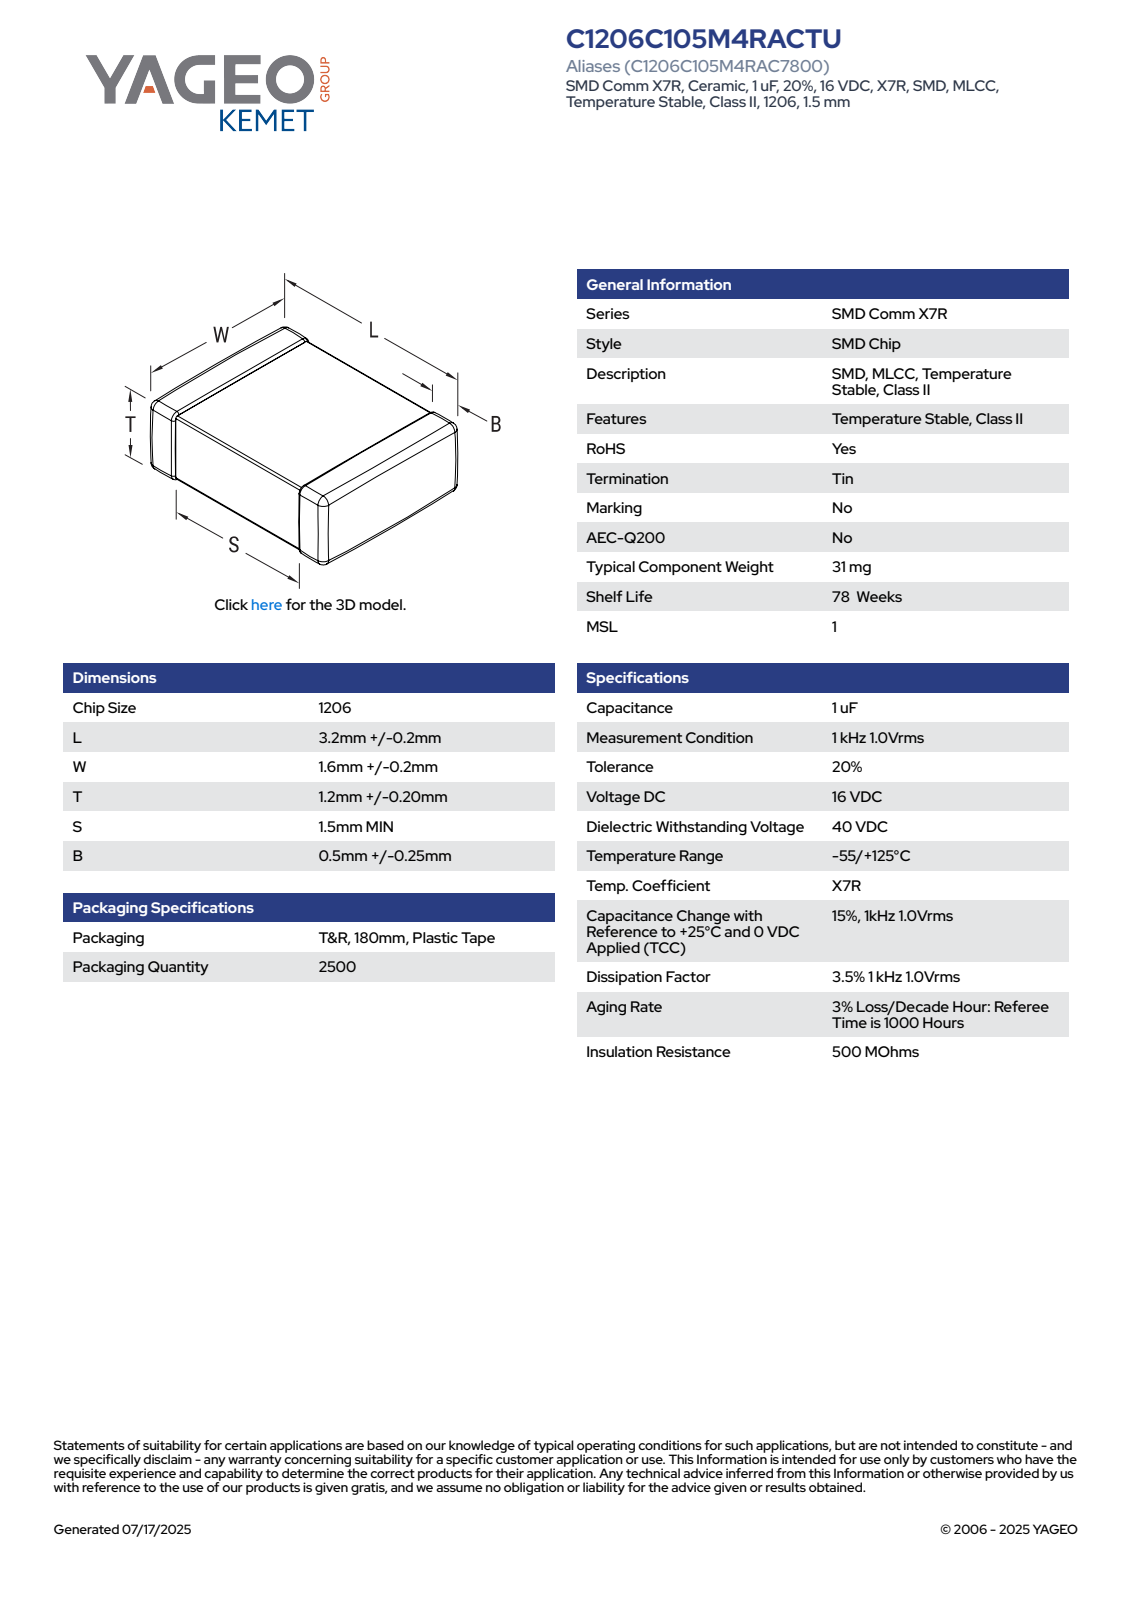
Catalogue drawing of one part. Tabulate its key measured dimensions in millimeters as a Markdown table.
| quantity | value |
| --- | --- |
| part name | CCS_CCSTD_1206_L3.4W1.8T1.4B0.5 |
| STEP written by | SolidWorks 2021 (AUTOMOTIVE_DESIGN) |
| units | millimeters |
| bodies | 4 solids, 125 faces (71 planar, 38 cylindrical, 16 other) |
| overall size | 3.4 × 1.8 × 1.4 |
| volume | 8 mm³ |
| surface area | 27 mm² |
| main face-to-face distances | 1.36, 1.76, 1.32, 1.72, 1.4, 3.4, 1.8, 1.37, 1.33, 1.57 |
